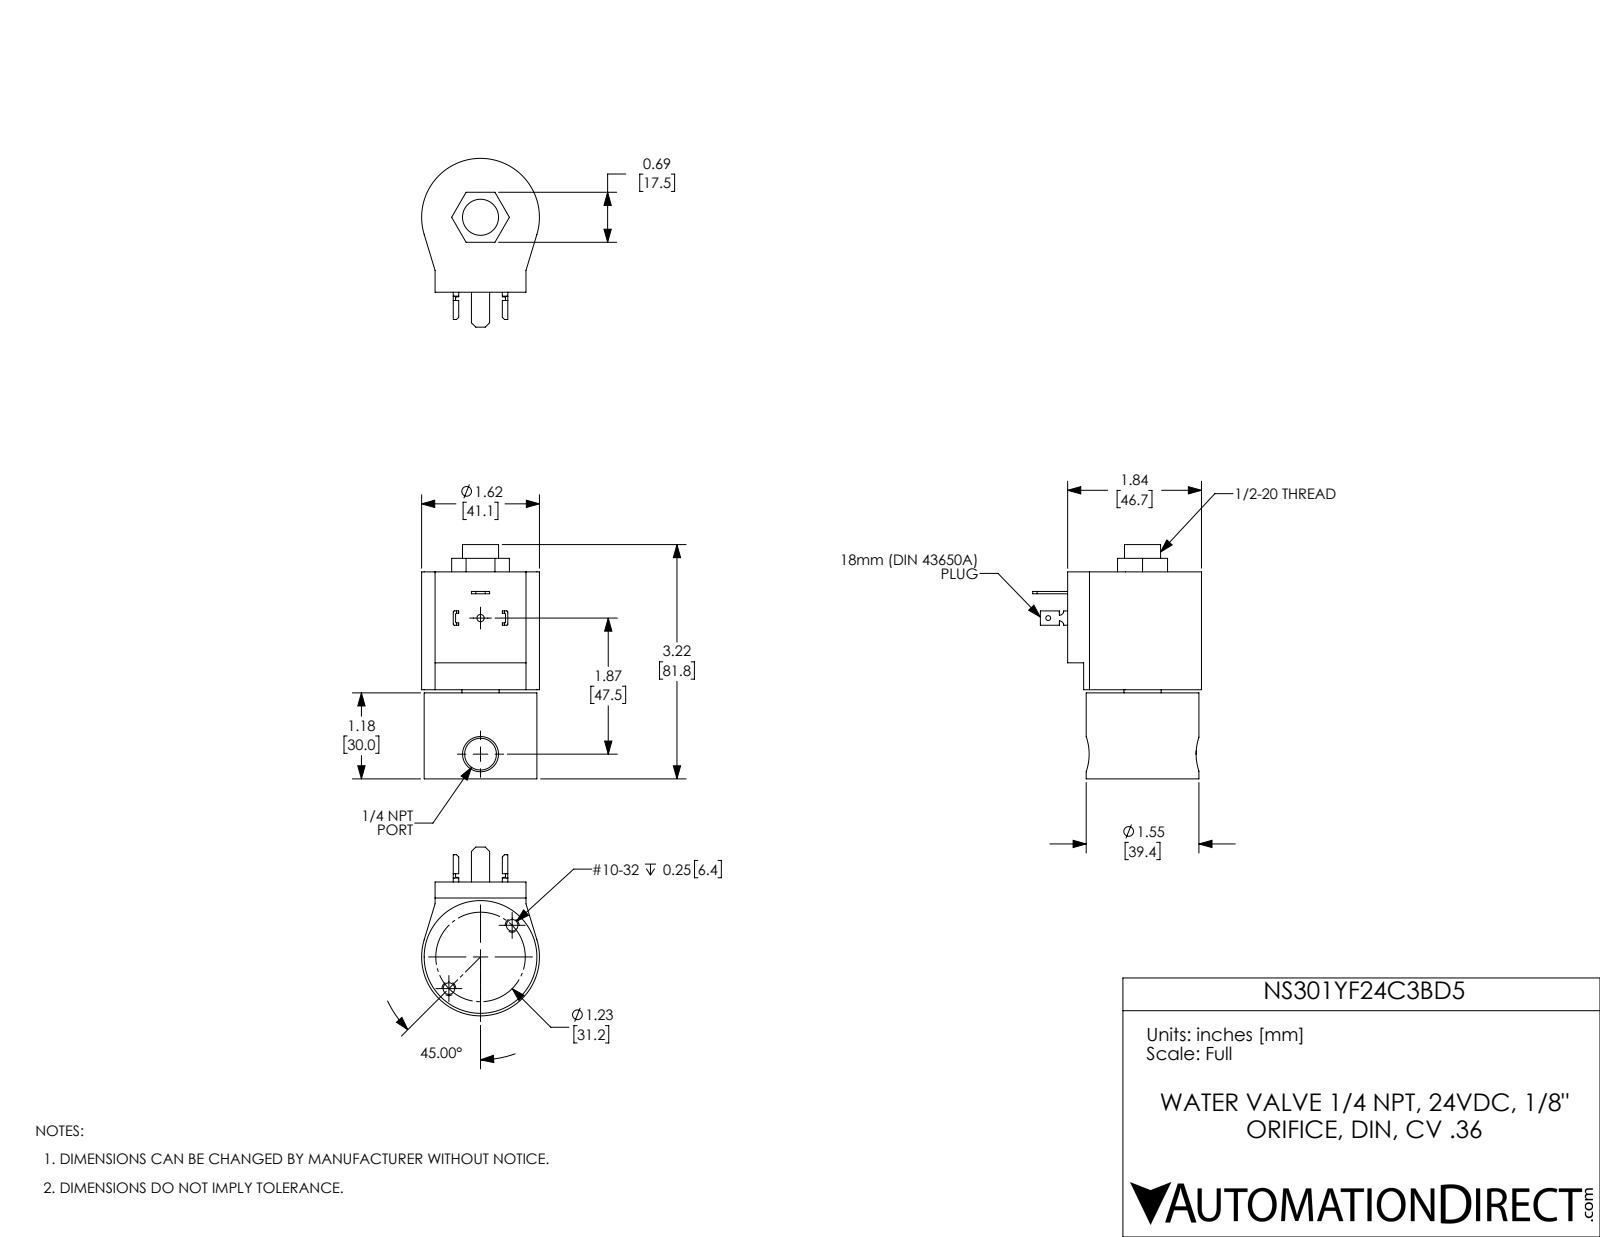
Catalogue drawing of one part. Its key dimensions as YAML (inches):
part_name: "NS301YF16C3BD5"
step_written_by: "SolidWorks 2017 (AUTOMOTIVE_DESIGN)"
units: inches
bodies: {solids: 6, faces: 130, planar: 73, cylindrical: 49, other: 8}
overall_size: [3.22, 2.32, 1.62]
volume: 6.042
surface_area: 33.19
round_holes:
  - {diameter: 0.159, count: 2}
  - {diameter: 0.067, count: 1}
  - {diameter: 0.1, count: 1}
  - {diameter: 0.437, count: 1}
  - {diameter: 0.496, count: 1}
  - {diameter: 0.512, count: 1}
  - {diameter: 1.155, count: 1}
round_bosses_or_shafts:
  - {diameter: 1.55, count: 1}
partial_cylinders:
  - {radius: 0.015, count: 8}
  - {radius: 0.06, count: 2}
  - {radius: 0.81, count: 1}
face_to_face_distances: [2.845, 1.182, 1.663, 1.225, 0.043, 1.62, 1.287, 0.106, 0.062, 1.558]
hole_center_spacings: [0.615, 1.23, 1.87]
